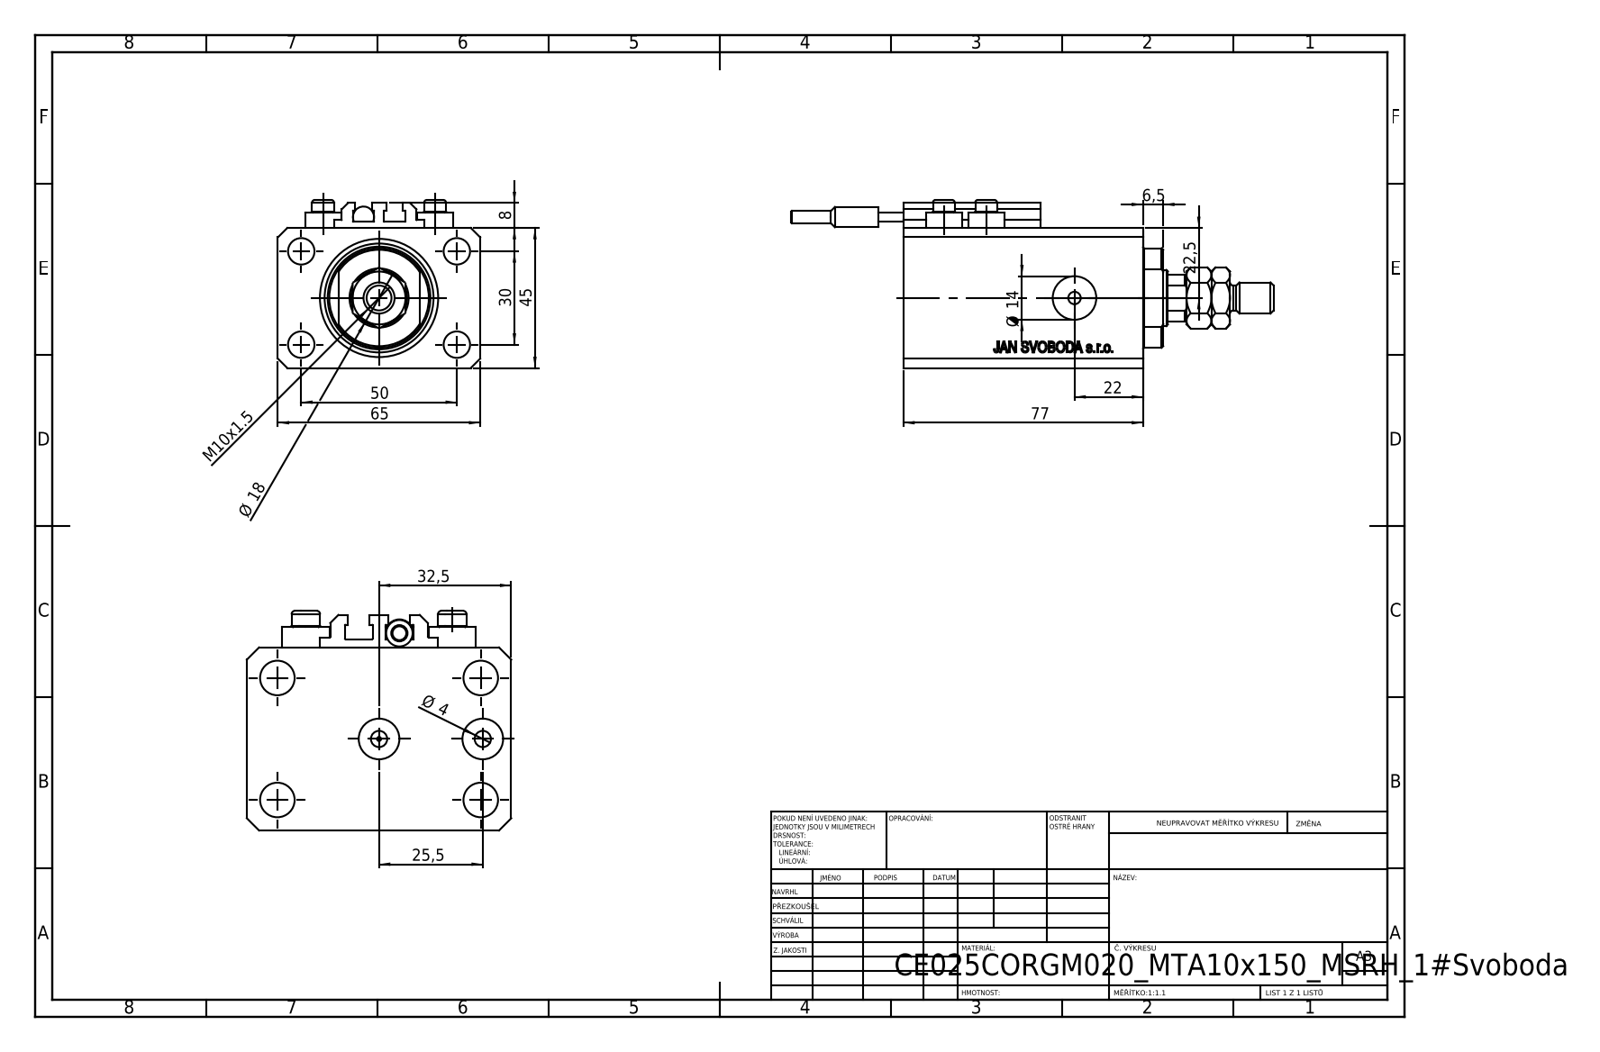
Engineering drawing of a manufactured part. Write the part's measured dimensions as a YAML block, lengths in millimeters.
part_name: "V250CE_C_VCP; MTA; SWITCH_V250CE; V250CE_C_Body (+2 more)"
step_written_by: "SolidWorks 2019 (CONFIG_CONTROL_DESIGN)"
units: millimeters
bodies: {solids: 10, faces: 1117, planar: 535, cylindrical: 102, other: 480}
overall_size: [155, 65, 54]
volume: 217774
surface_area: 60793
round_holes:
  - {diameter: 4, count: 8}
  - {diameter: 8.5, count: 5}
  - {diameter: 10, count: 2}
  - {diameter: 14, count: 2}
  - {diameter: 1.25, count: 1}
  - {diameter: 18, count: 1}
  - {diameter: 25, count: 1}
  - {diameter: 38, count: 1}
round_bosses_or_shafts:
  - {diameter: 11.6, count: 4}
  - {diameter: 7, count: 4}
  - {diameter: 8, count: 1}
  - {diameter: 6.8, count: 1}
  - {diameter: 6.5, count: 1}
  - {diameter: 4, count: 1}
partial_cylinders:
  - {radius: 0.2, count: 10}
  - {radius: 8.5, count: 1}
  - {radius: 16, count: 1}
face_to_face_distances: [45, 65, 14, 77, 63, 6.9, 3, 47, 56.1, 70.1]
hole_center_spacings: [29.15, 13.6, 15.01, 30, 36, 38.48, 50, 52.68]
